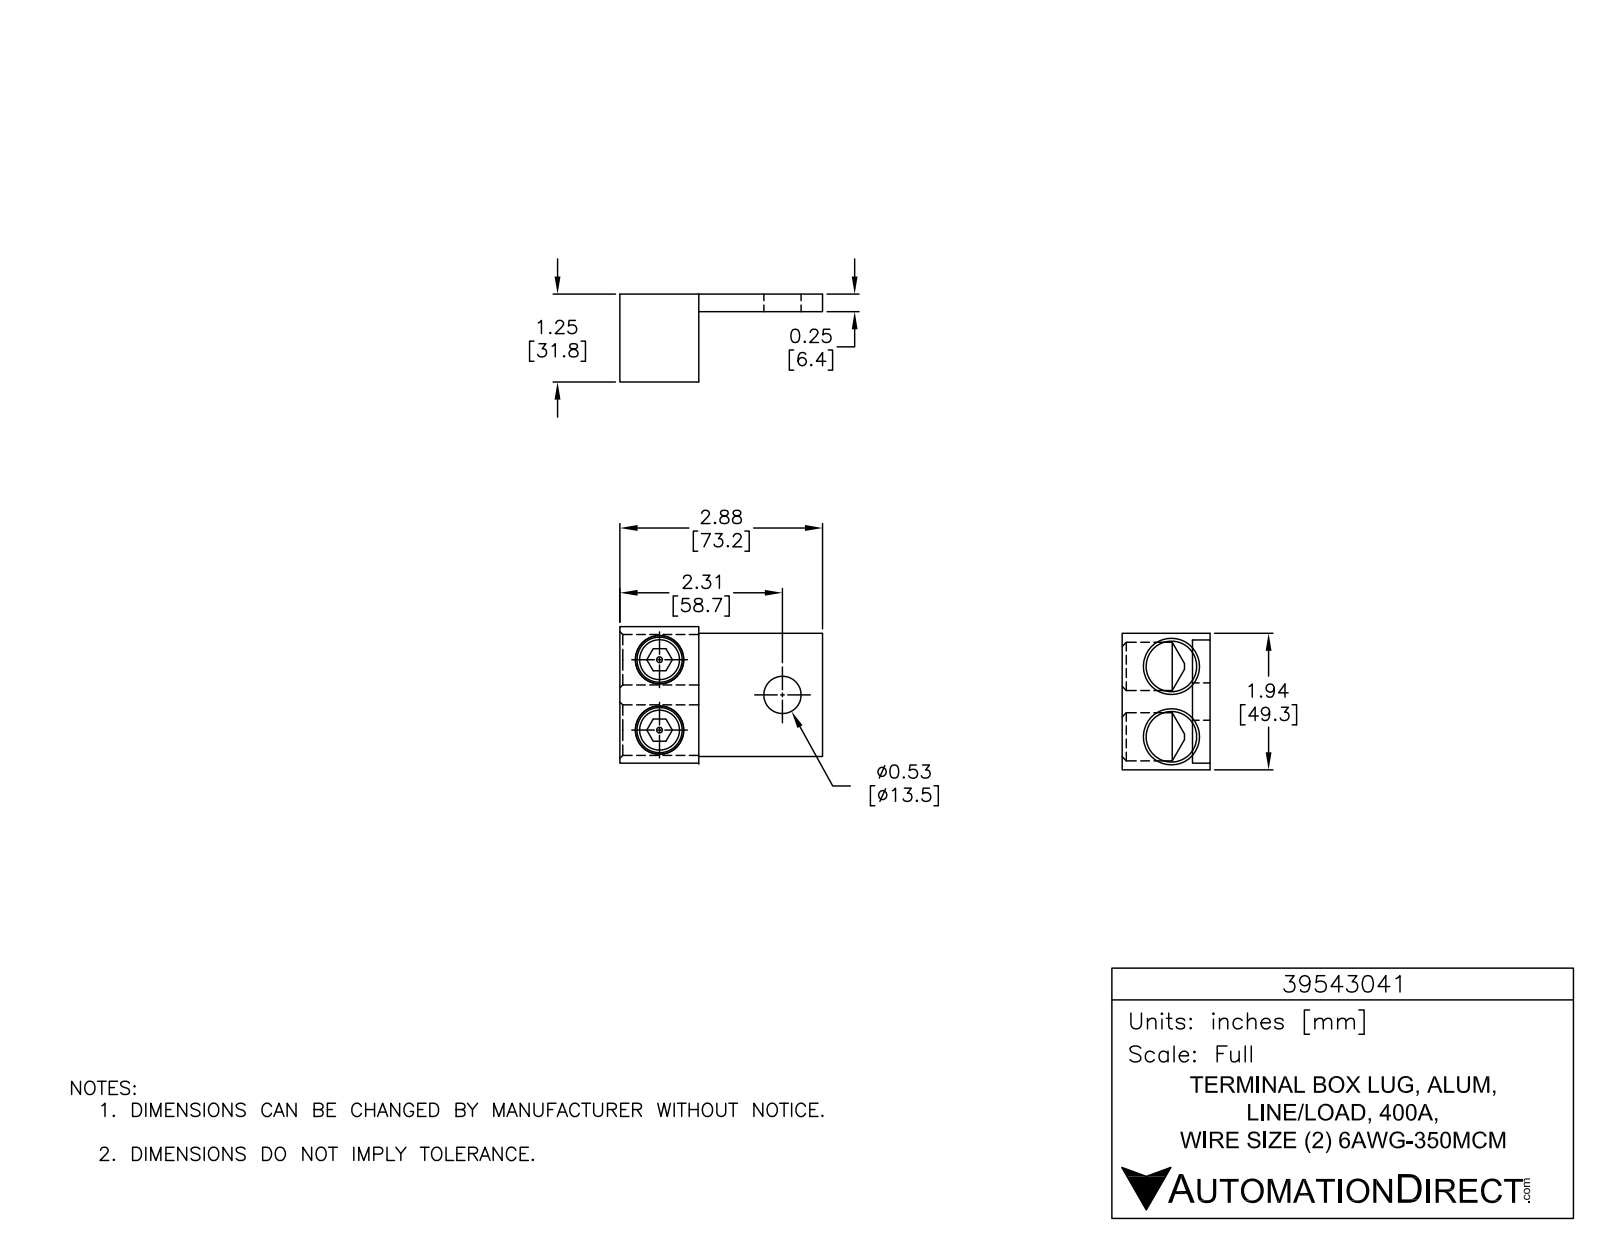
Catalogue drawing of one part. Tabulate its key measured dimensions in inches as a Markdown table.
| quantity | value |
| --- | --- |
| part name | 39543041 |
| STEP written by | SolidWorks 2015 (AUTOMOTIVE_DESIGN) |
| units | inches |
| bodies | 3 solids, 60 faces (28 planar, 14 cylindrical, 18 other) |
| overall size | 2.88 × 1.94 × 1.25 |
| volume | 2.749 in³ |
| surface area | 28.29 in² |
| round holes (diameter × count) | 0.642 × 2, 0.718 × 2, 0.53 × 1 |
| round bosses / shafts (diameter × count) | 0.685 × 2 |
| main face-to-face distances | 0.25, 1, 1.25, 1.94, 1.12, 0.095, 1.845, 0.315, 1.75, 1.76 |
| hole center spacings | 1, 1.817 |
